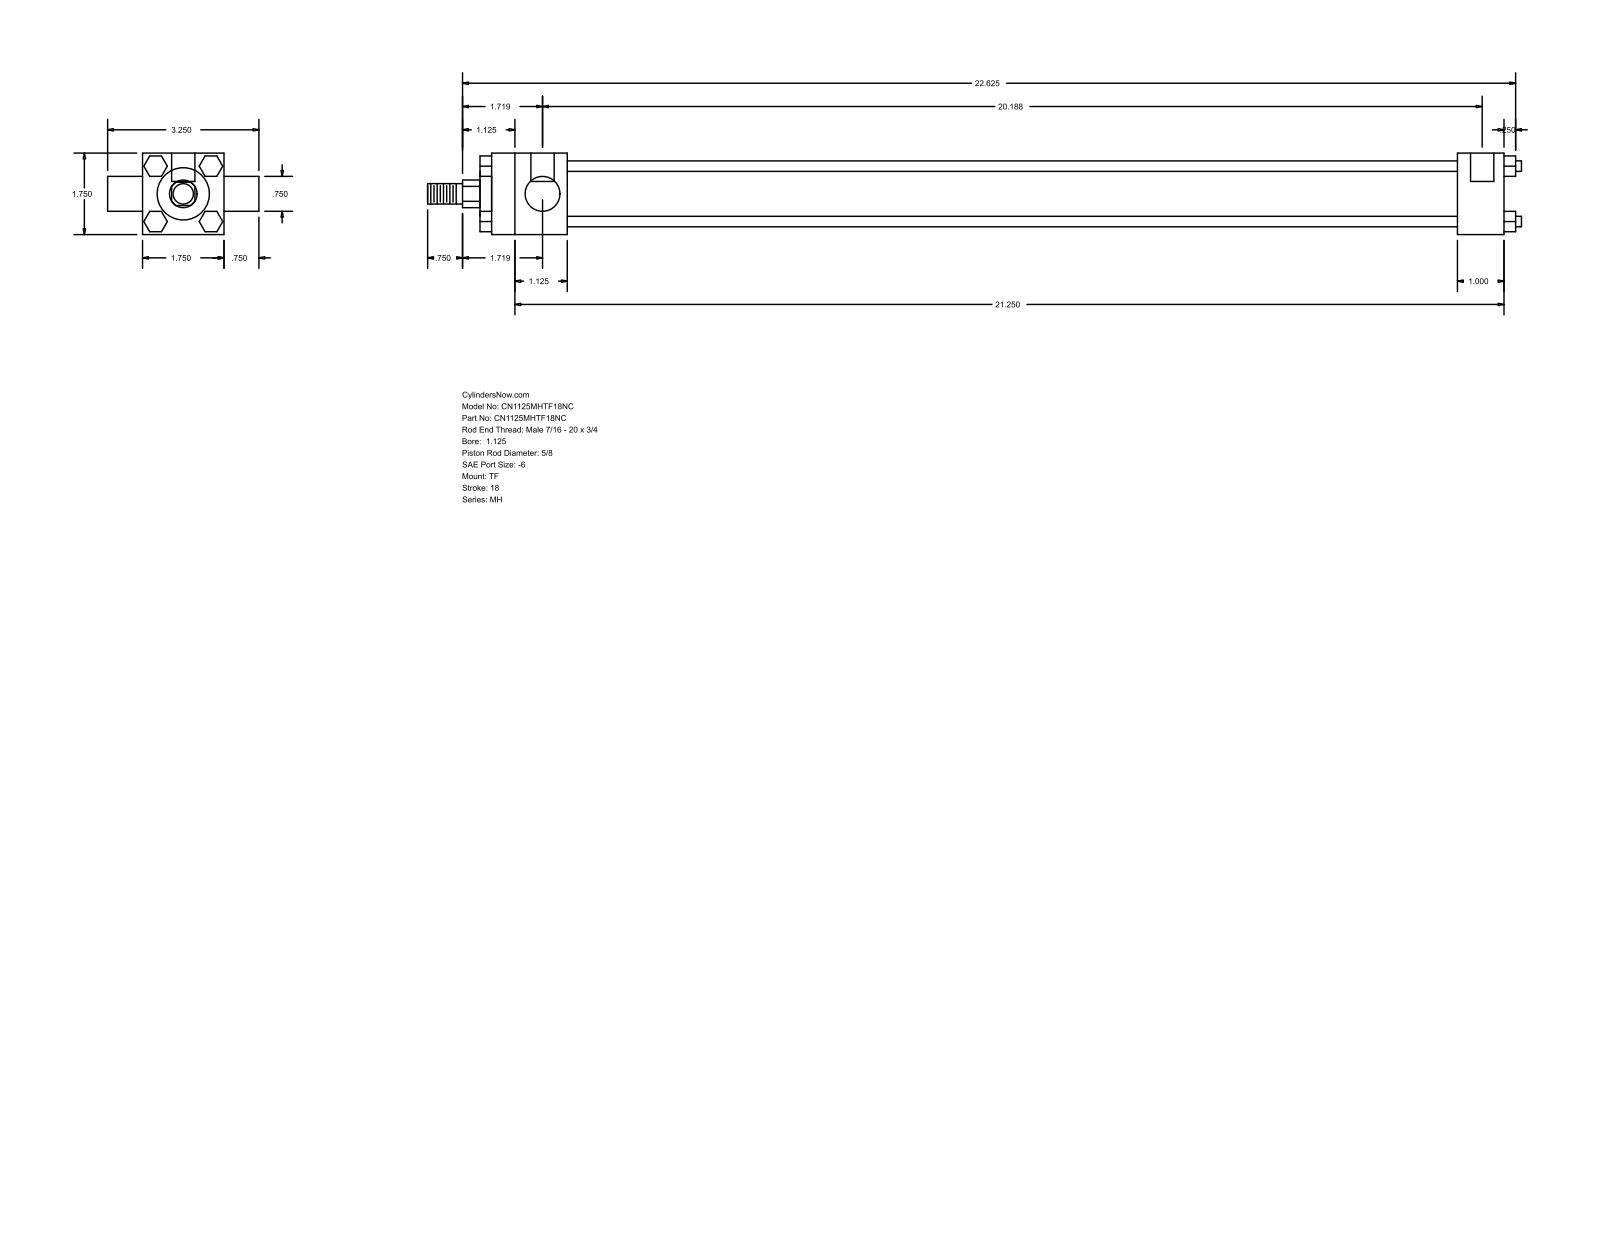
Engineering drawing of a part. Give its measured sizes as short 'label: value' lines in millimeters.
name: MH_TF__0112_0.625
written by: GSSL Pune (CONFIG_CONTROL_DESIGN)
unit: mm
bodies: 0 solids, 120 faces (92 planar, 28 cylindrical, 0 other)
size: 596.9 × 82.55 × 44.45
holes: 3× ⌀5.56, 2× ⌀12.7
bosses: 4× ⌀5.71, 1× ⌀34.92, 1× ⌀28.57, 1× ⌀19.05, 1× ⌀15.88, 1× ⌀11.11
rounds: 1× R7.54
face distances: 44.46, 11.11, 485.77, 511.18, 25.41, 41.27, 527.04, 552.45, 47.62, 6.35
hole spacings: 3.17, 509.59, 512.76
